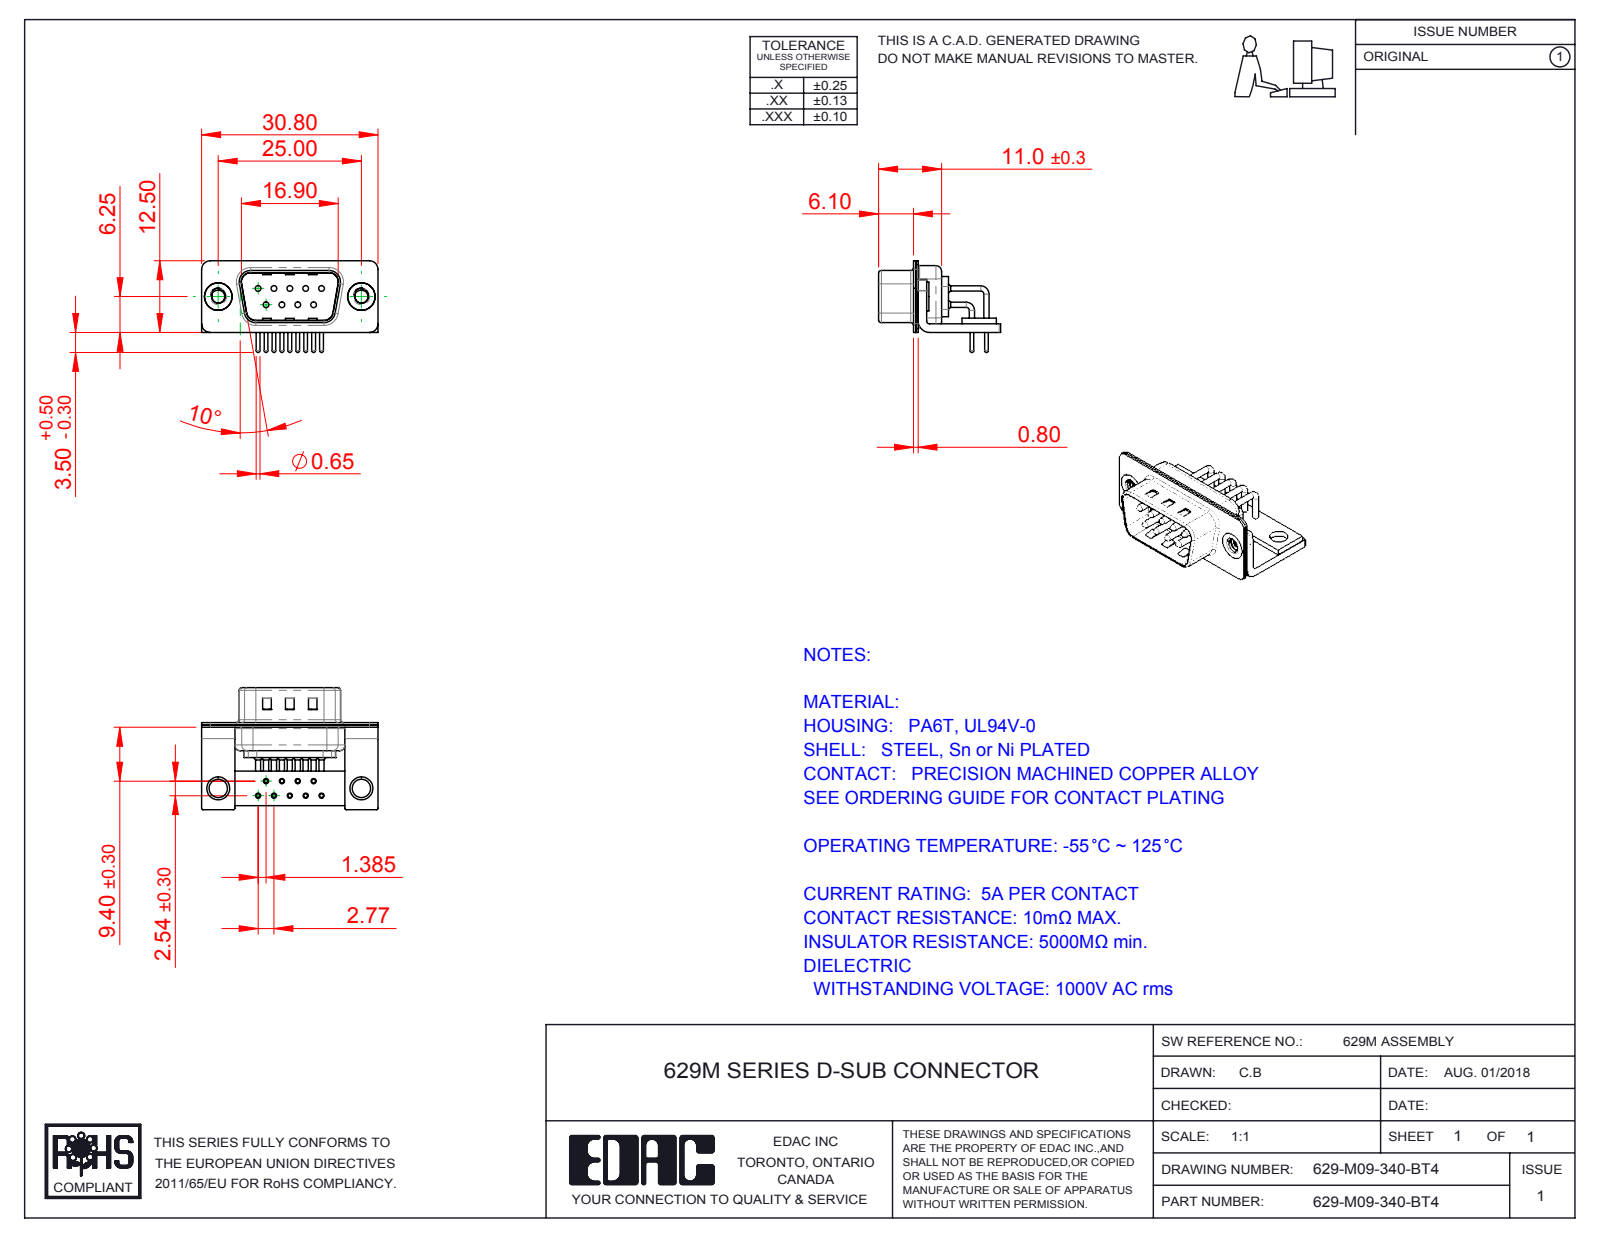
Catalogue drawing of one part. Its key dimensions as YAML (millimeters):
part_name: "629M Stabilizer Board_09 Contacts; 629M Stabilizer Bracket; 629M 4-40 Threaded Rivet_Stabilizer; 629M Contact Row 2 (+5 more)"
step_written_by: "SolidWorks 2016 (CONFIG_CONTROL_DESIGN)"
units: millimeters
bodies: {solids: 17, faces: 1362, planar: 709, cylindrical: 493, other: 160}
overall_size: [30.8, 21.3, 16]
volume: 1810
surface_area: 4941
round_holes:
  - {diameter: 0.9, count: 9}
  - {diameter: 1, count: 9}
  - {diameter: 1.7, count: 9}
  - {diameter: 2, count: 9}
  - {diameter: 2.26, count: 2}
  - {diameter: 3.2, count: 2}
  - {diameter: 4, count: 2}
  - {diameter: 4.8, count: 2}
round_bosses_or_shafts:
  - {diameter: 1.5, count: 9}
  - {diameter: 0.9, count: 9}
  - {diameter: 0.65, count: 9}
  - {diameter: 5, count: 2}
  - {diameter: 4.9, count: 2}
partial_cylinders:
  - {radius: 0.25, count: 16}
  - {radius: 1.5, count: 16}
  - {radius: 2, count: 13}
  - {radius: 0.5, count: 9}
  - {radius: 1.01, count: 9}
  - {radius: 1.6, count: 8}
  - {radius: 0.6, count: 4}
  - {radius: 0.65, count: 4}
face_to_face_distances: [0.4, 1.5, 0.8, 0.85, 1.25, 1.9, 1, 2.5, 10.4, 9.55]
hole_center_spacings: [2.77, 5.54, 3.16, 4.87, 8.31, 2.89, 2.9, 5.03]
